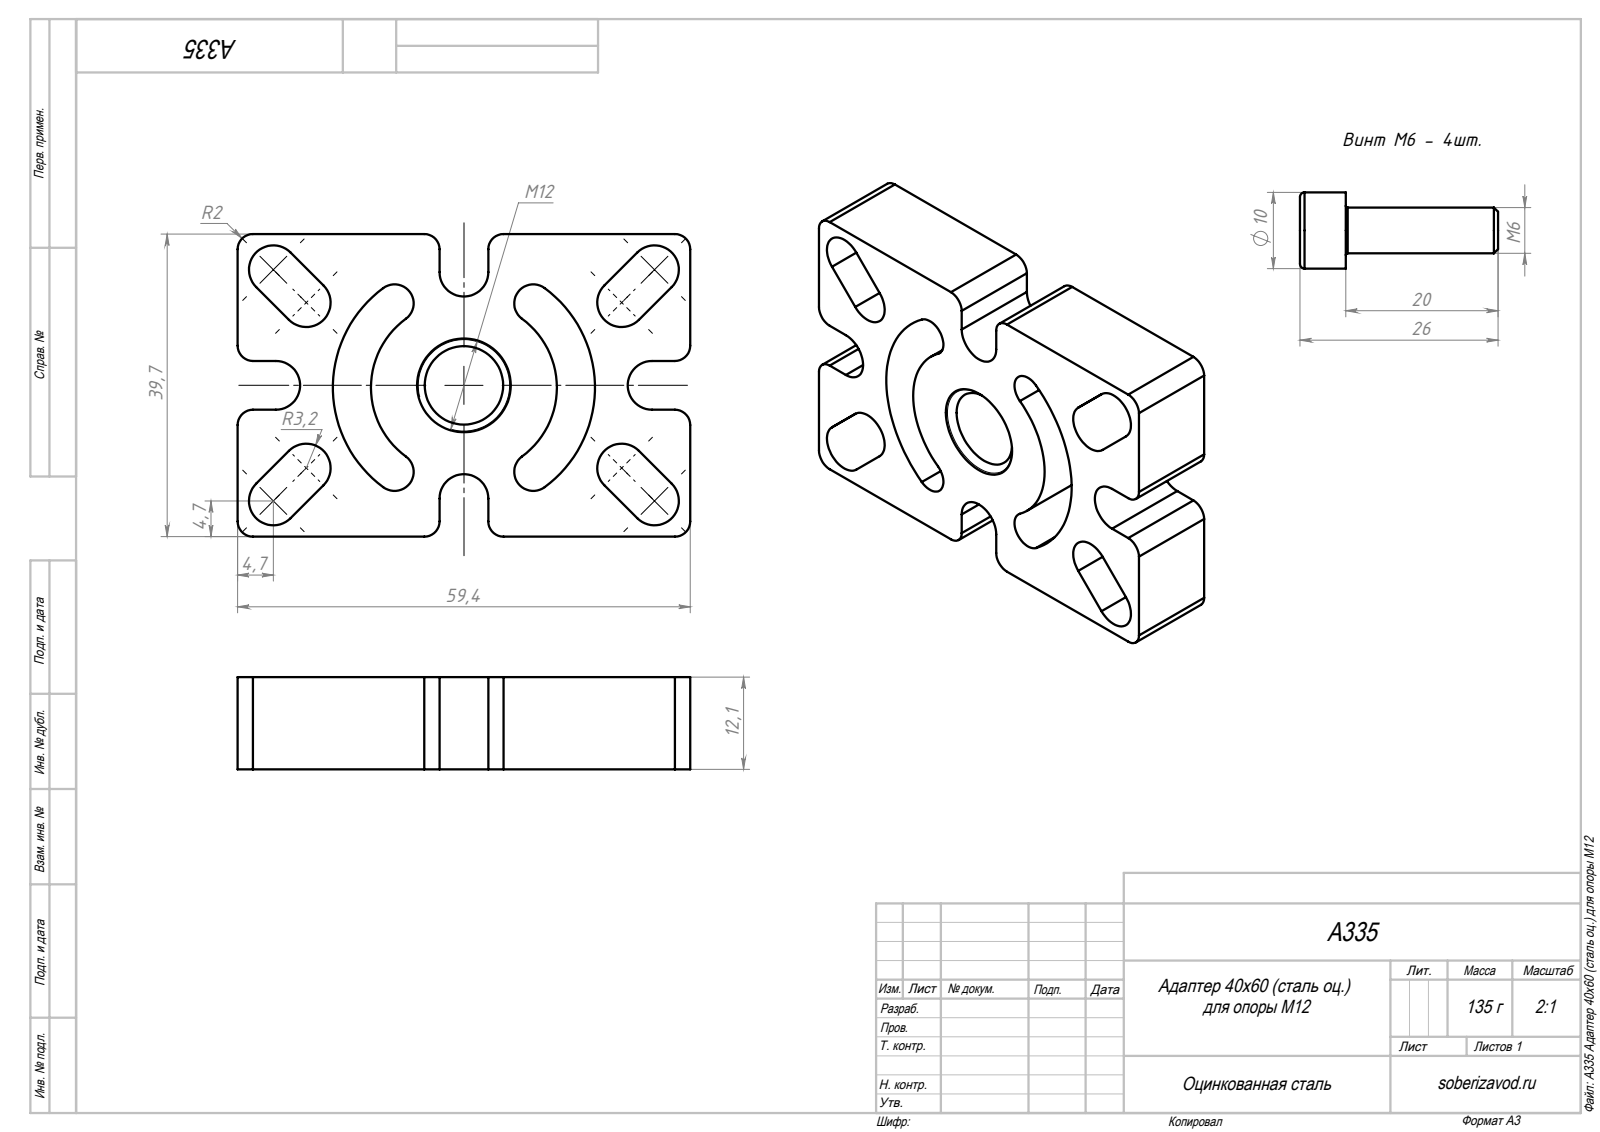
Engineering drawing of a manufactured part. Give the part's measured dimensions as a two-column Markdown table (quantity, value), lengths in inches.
| quantity | value |
| --- | --- |
| part name | A335 Адаптер 40х60 (Алюм) для опоры М12, Винт(1)_00; A335 Адаптер 40х60 (сталь оц.) для опоры М12_00; A335 Адаптер 40х60 (сталь оц.) для опоры М12 |
| STEP written by | SolidWorks 2018 (AUTOMOTIVE_DESIGN) |
| units | inches |
| bodies | 5 solids, 165 faces (70 planar, 67 cylindrical, 28 other) |
| overall size | 2.363 × 1.588 × 1.024 |
| volume | 1.33 in³ |
| surface area | 19.23 in² |
| round holes (diameter × count) | 0.039 × 4, 0.406 × 1 |
| round bosses / shafts (diameter × count) | 0.394 × 4, 0.236 × 4 |
| partial cylindrical surfaces (radius × count) | 0.079 × 12, 0.126 × 12, 0.098 × 4, 0.441 × 2, 0.638 × 2 |
| main face-to-face distances | 0.476, 1.563, 0.252, 2.339, 0.548, 0.118, 0.296, 0.8, 0.656, 0.907 |
| hole center spacings | 1.152, 1.194, 1.969, 2.303 |
